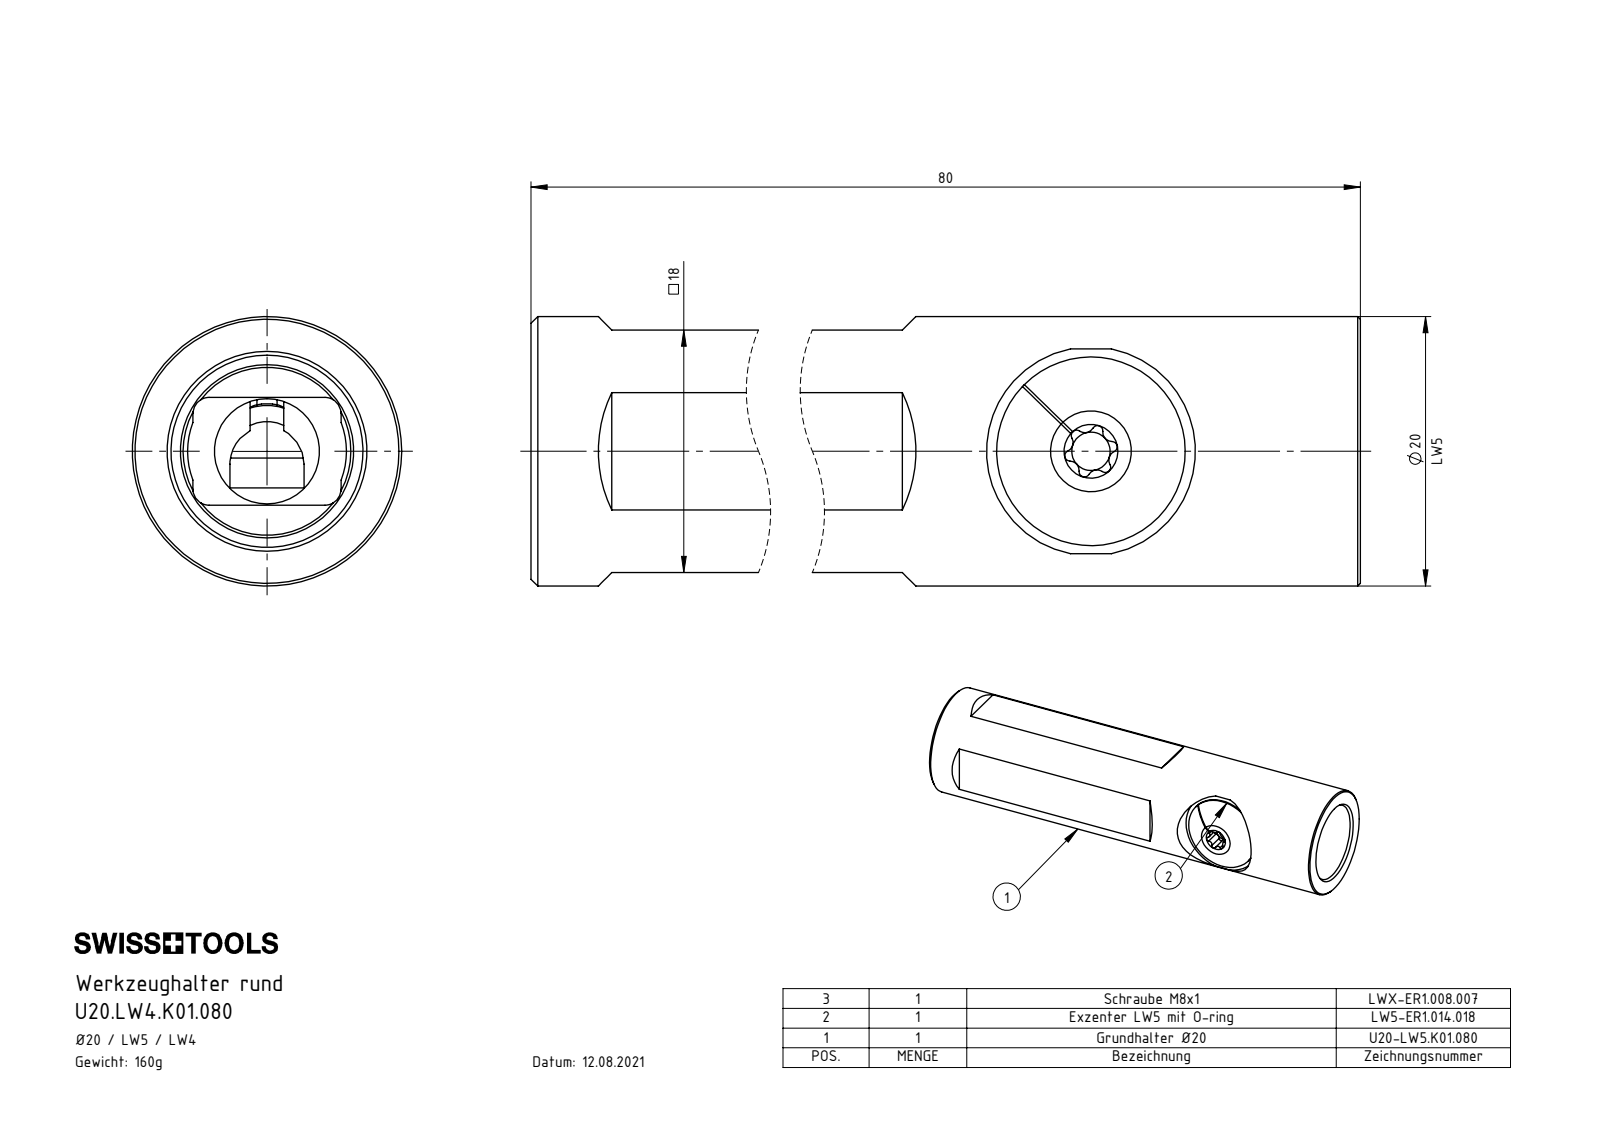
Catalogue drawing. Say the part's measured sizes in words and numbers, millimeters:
The part is named "U20-LW5.K01.080_C; LW5-ER1.014.018_B_Standard<Wie bearbeitet>; LWX-ER1.008.007_A; DIN 3771 - 10x1 (+2 more)". Its 3-D file was written by "SolidWorks 2022 (CONFIG_CONTROL_DESIGN)". It is 5 solids with 216 faces: 62 planar, 87 cylindrical and 67 other. Overall it measures 80 by 20 by 20 millimeters. Its volume is 20 439 cubic millimeters and its surface area 8 946 square millimeters. Round holes: 1 of diameter 1, 1 of diameter 2.4, 1 of diameter 2.85, 1 of diameter 5, 1 of diameter 7, 1 of diameter 7.8, 1 of diameter 12.86, 1 of diameter 15.5. Round bosses or shafts: 1 of diameter 20, 1 of diameter 14, 1 of diameter 12, 1 of diameter 10.2, 1 of diameter 8, 1 of diameter 6.5. Partial cylindrical surfaces (rounded edges, fillets, slot ends): 6 of radius 0.34, 6 of radius 0.4, 6 of radius 0.59, 6 of radius 0.69, 4 of radius 1.2, 2 of radius 2.75, 1 of radius 4.1, 1 of radius 4.15. The main face-to-face distances are 18, 14.5, 2.5, 80, 1, 2.4, 15.6, 17, 1.4, 12.1.
